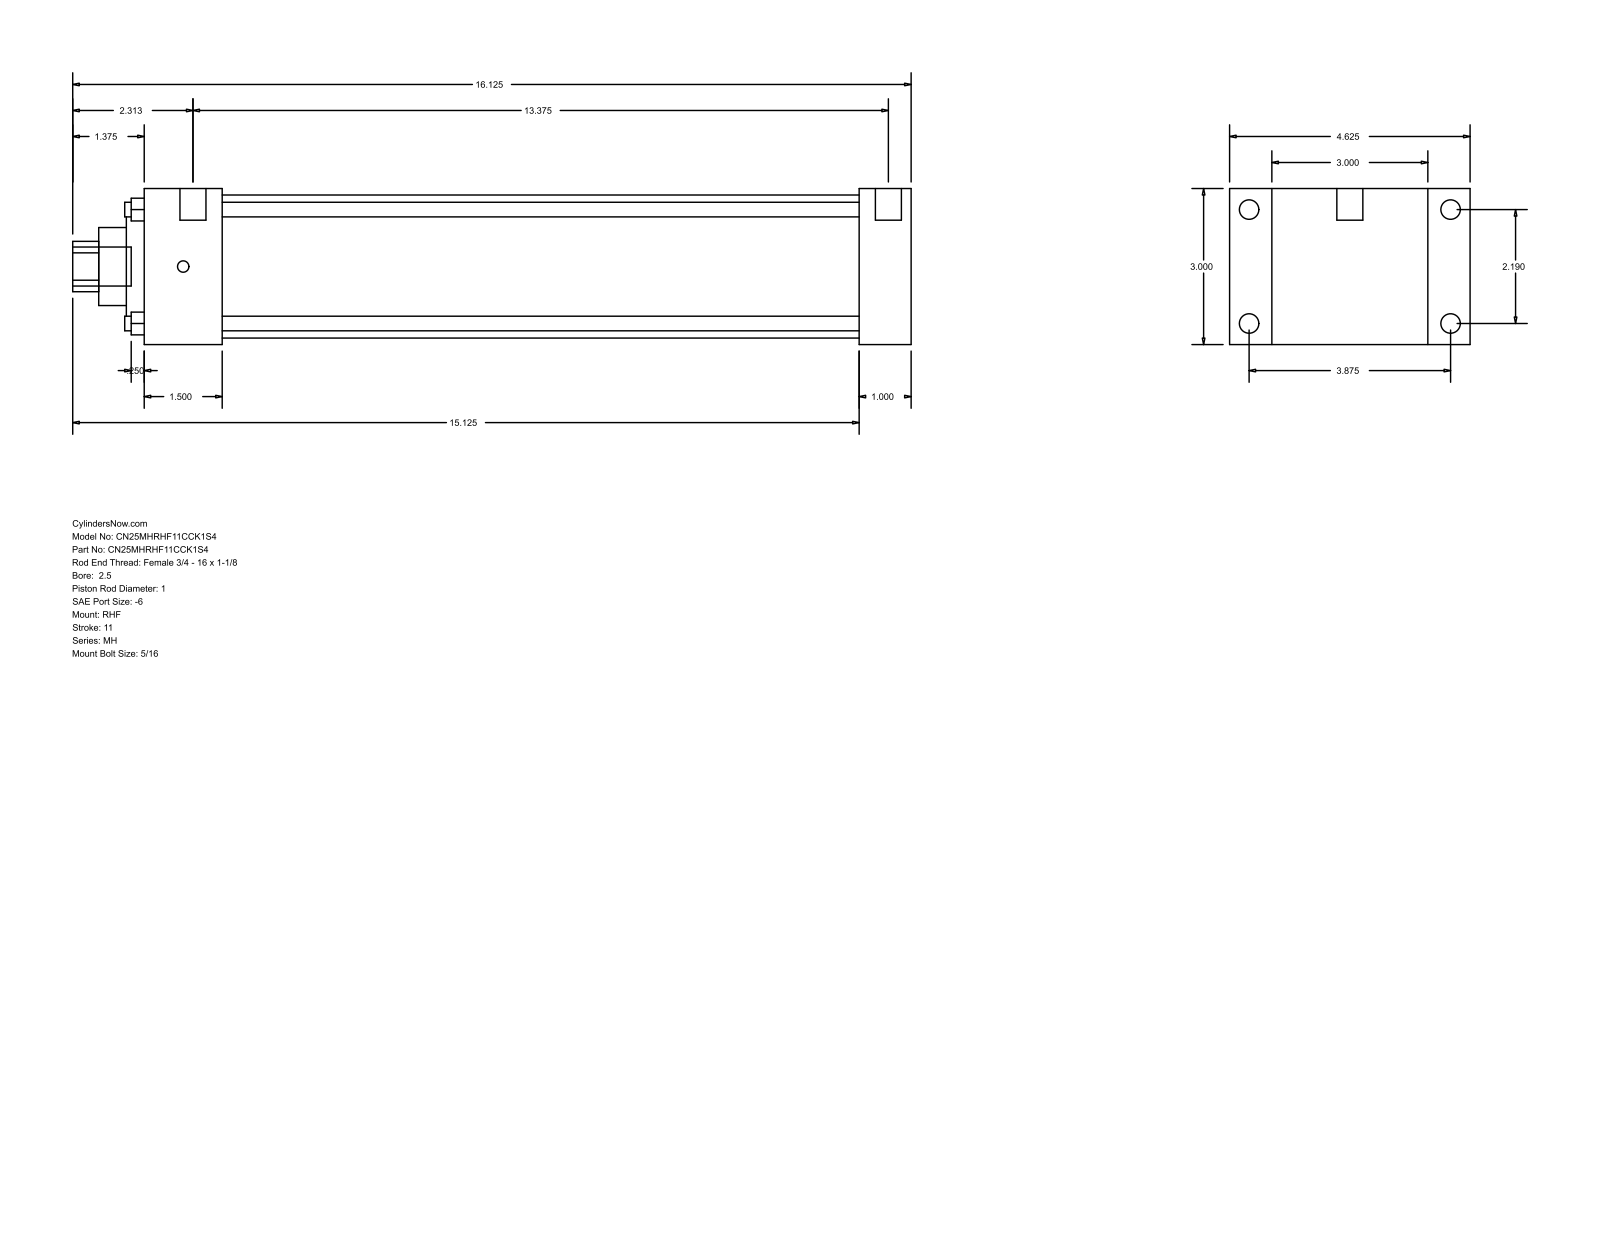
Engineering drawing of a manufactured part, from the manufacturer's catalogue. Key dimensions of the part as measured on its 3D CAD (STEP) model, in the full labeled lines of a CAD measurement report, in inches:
Part name (STEP PRODUCT): MH_RHF__0250_1
STEP written by: GSSL Pune (CONFIG_CONTROL_DESIGN)
Units: inches
Bodies: 0 solids, 90 faces (61 planar, 29 cylindrical, 0 other)
Overall size (bounding box): 16.125 × 4.625 × 3
Round holes (diameter × count): ⌀0.281 ×4, ⌀1 ×1, ⌀1.5 ×1, ⌀2.375 ×1, ⌀2.75 ×1
Round bosses / shafts (diameter × count): ⌀0.375 ×4, ⌀0.219 ×4, ⌀0.5 ×2, ⌀0.75 ×1
Partial cylindrical surfaces — rounded edges, fillets, slot ends (radius × count): R0.484 ×1
Main face-to-face distances: 3, 1, 0.813, 3.813, 14.75, 13.75, 4.625, 1.5, 12.25, 13.25
Hole centre spacings: 1.548, 2.19, 3.097
